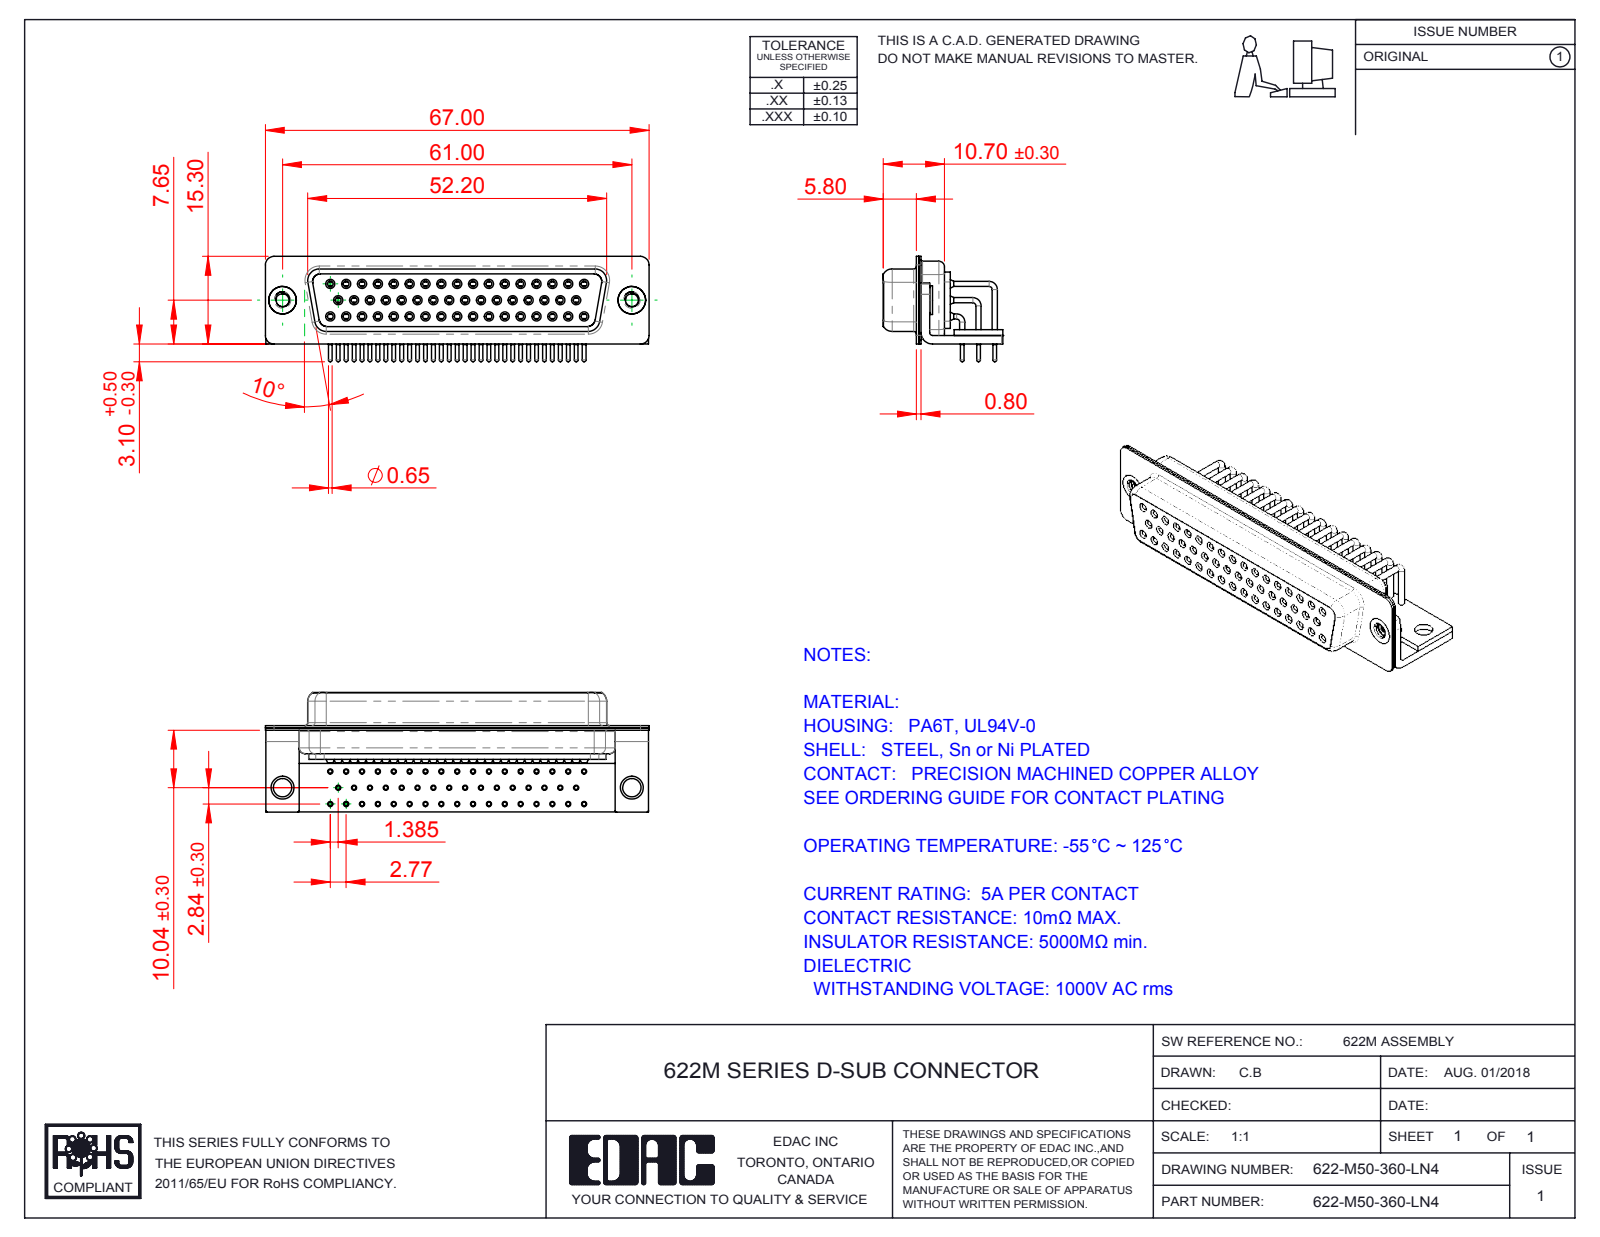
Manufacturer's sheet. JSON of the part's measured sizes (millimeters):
{"part_name": "622M Shell Rear_50 Contacts; 622M Shell Front_50 Contacts; 622M Housing_50 Contacts; 622-M50-360-LN4 (+6 more)", "step_written_by": "SolidWorks 2016 (CONFIG_CONTROL_DESIGN)", "units": "millimeters", "bodies": {"solids": 58, "faces": 3079, "planar": 843, "cylindrical": 1409, "other": 827}, "overall_size": [67, 20.9, 18.4], "volume_mm3": 7744, "surface_area_mm2": 18114, "round_holes": [[0.9, 50], [1, 50], [1.1, 50], [1.7, 50], [1.8, 50], [2, 50], [2.26, 2], [3.2, 2], [4, 2], [4.8, 2]], "round_bosses_or_shafts": [[0.9, 59], [1.6, 50], [1.5, 50], [0.65, 50], [5, 2], [4.9, 2]], "partial_cylinders_radius": [[0.25, 16], [1.5, 16], [2, 13], [1.35, 8], [1.6, 8], [0.5, 5], [0.6, 4], [0.65, 4]], "face_to_face_distances": [0.4, 1, 2.2, 0.85, 1.35, 11.85, 12.25, 5.8, 5.9, 0.8], "hole_center_spacings": [2.77, 3.16, 5.54, 8.31, 11.08, 13.85, 16.62, 19.39]}
